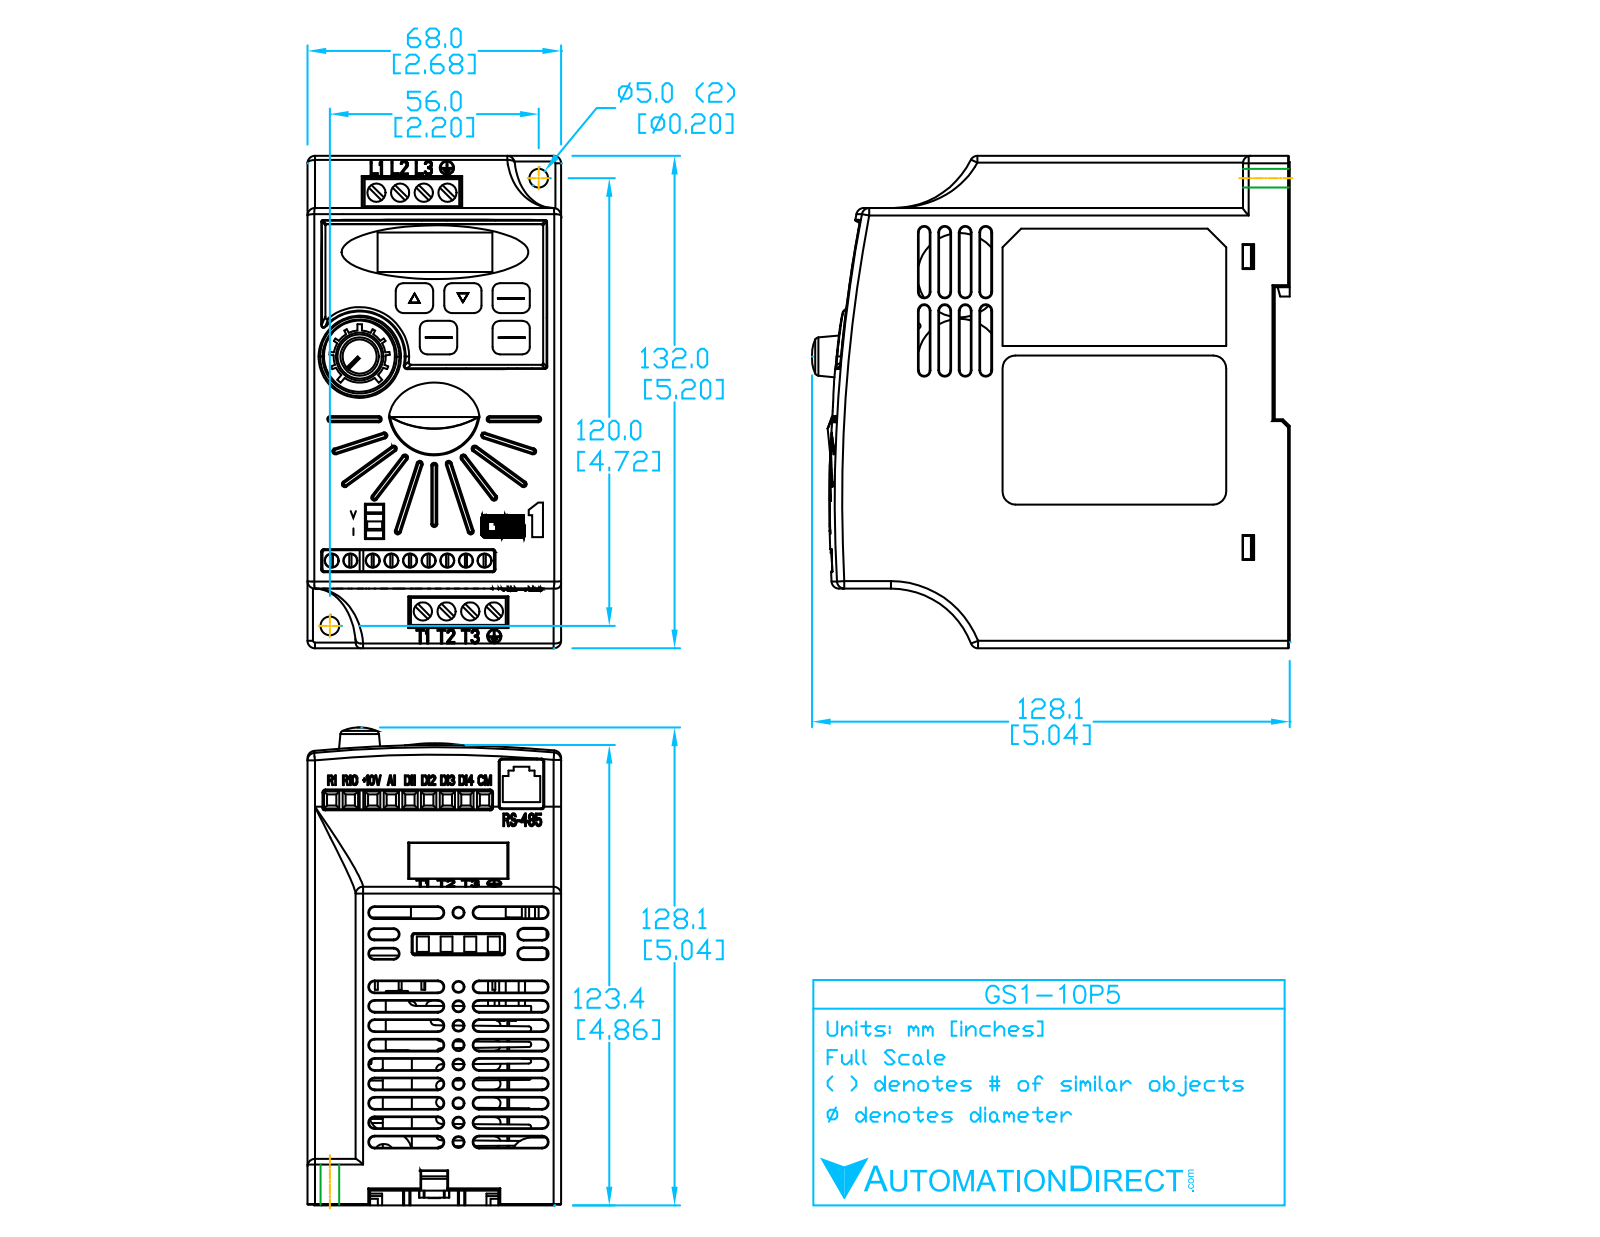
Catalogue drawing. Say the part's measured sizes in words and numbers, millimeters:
The part is named "GS1-10P5". Its 3-D file was written by "SolidWorks 2013 (AUTOMOTIVE_DESIGN)". It is 1 solid with 871 faces: 542 planar, 168 cylindrical and 161 other. Overall it measures 134.2 by 132.1 by 68.1 millimeters. Its volume is 1 008 000 cubic millimeters and its surface area 70 650 square millimeters. Round holes: 9 of diameter 3.8, 8 of diameter 4.7, 2 of diameter 5.1. Round bosses or shafts: 5 of diameter 8. Partial cylindrical surfaces (rounded edges, fillets, slot ends): 38 of radius 0.8, 22 of radius 2.5, 20 of radius 1.5, 6 of radius 1.6, 2 of radius 0.4, 2 of radius 2.4, 2 of radius 5.1, 2 of radius 11.2. The main face-to-face distances are 68.1, 4.4, 132.1, 0.4, 131.7, 4.2, 14, 118.1, 13.6, 15.7. The hole center spacings are 5.1, 10.2, 15.2, 20.3, 25.4, 30.5, 35.6, 99.6.
